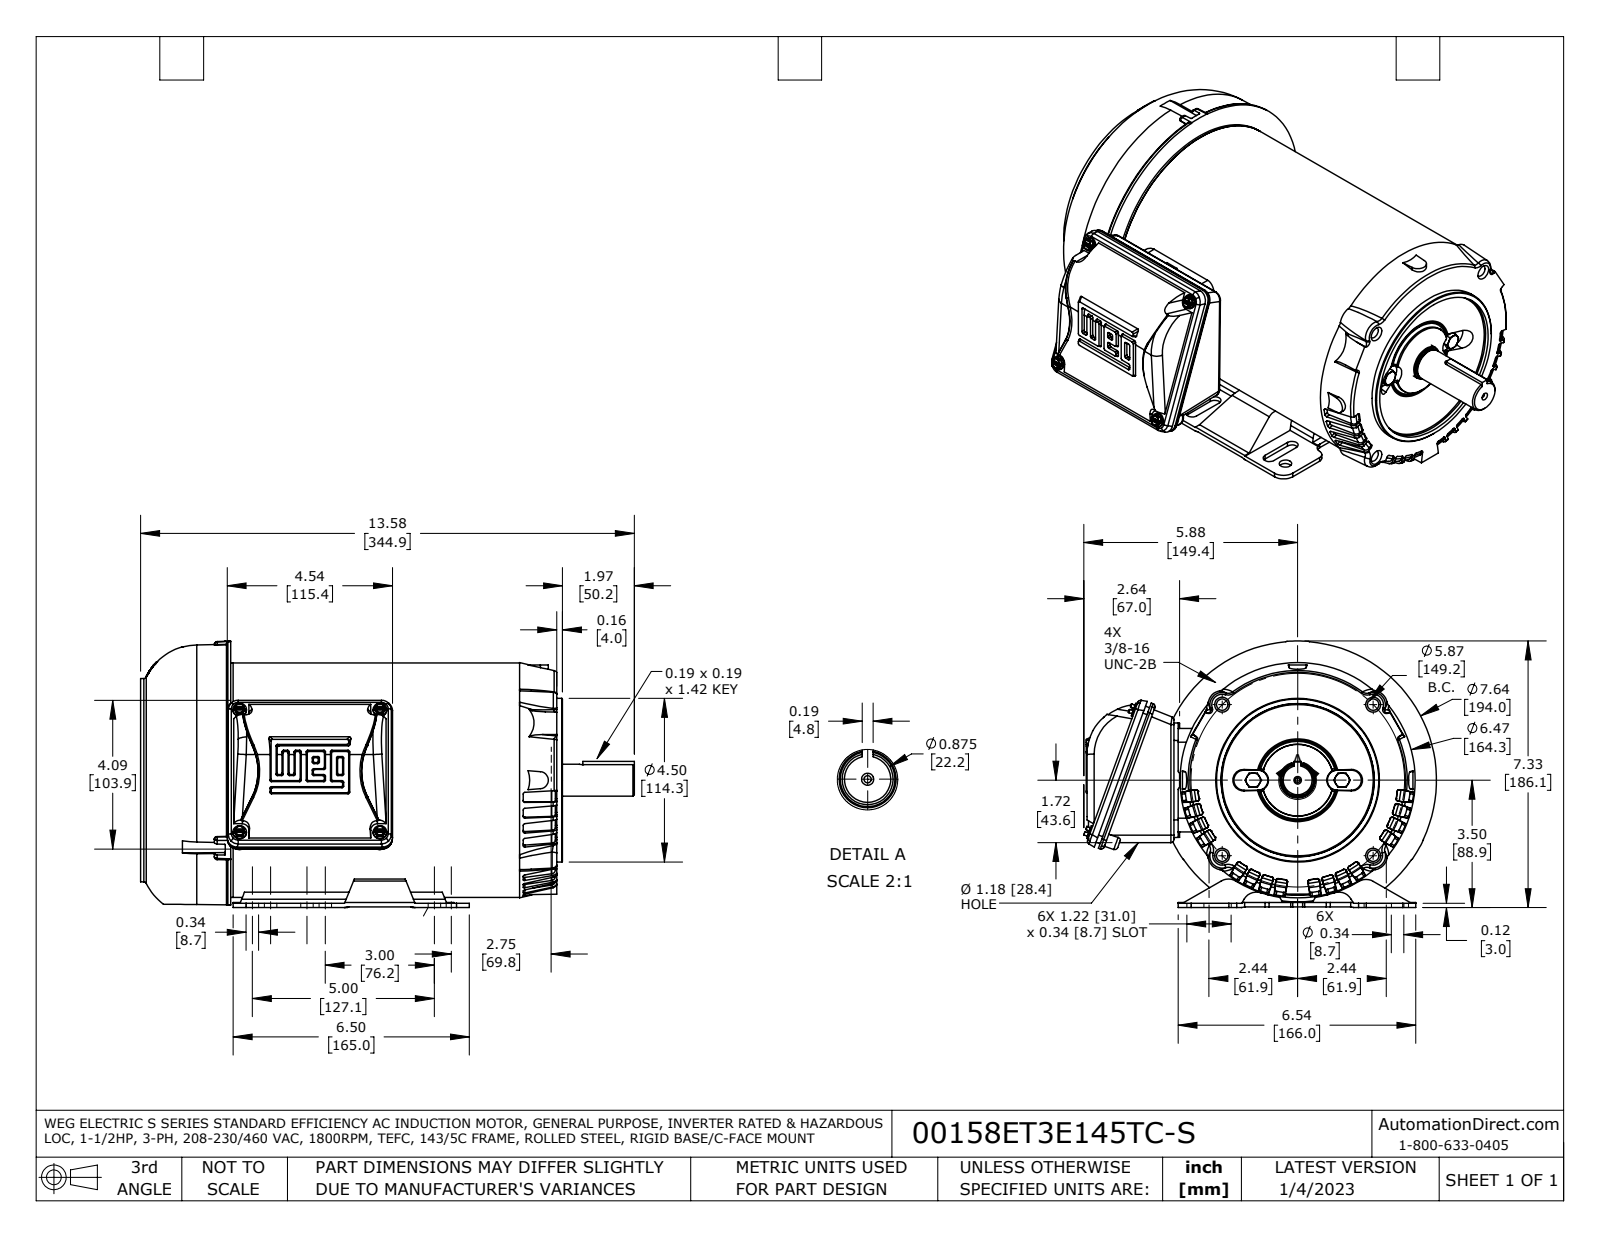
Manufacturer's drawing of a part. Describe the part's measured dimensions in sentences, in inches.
The part is named "143-5C_3PH_TEFC_GP_13583 broken base surfs w 1PHNB 1 fxt". Its 3-D file was written by "SolidWorks 2021 (AUTOMOTIVE_DESIGN)". It is 14 solids with 1478 faces: 552 planar, 352 cylindrical and 574 other. Overall it measures 13.577 by 9.7 by 7.551 inches. Its volume is 426.3 cubic inches and its surface area 724.1 square inches. Round holes: 6 of diameter 0.343, 4 of diameter 0.313, 1 of diameter 0.124. Round bosses or shafts: 4 of diameter 0.374, 2 of diameter 0.35, 1 of diameter 6.447, 1 of diameter 6.447, 1 of diameter 5.591, 1 of diameter 4.5, 1 of diameter 0.98, 1 of diameter 0.875. Partial cylindrical surfaces (rounded edges, fillets, slot ends): 40 of radius 0.047, 38 of radius 0.006, 32 of radius 0.051, 12 of radius 0.059, 12 of radius 0.087, 12 of radius 0.171, 10 of radius 0.02, 8 of radius 0.079. The main face-to-face distances are 7.874, 0.12, 0.067, 7.941, 2.283, 2.35, 10.224, 11.248, 8.965, 8.898. The hole center spacings are 2.937, 4.154, 5.5, 1, 4, 5, 5.59, 5.874.
